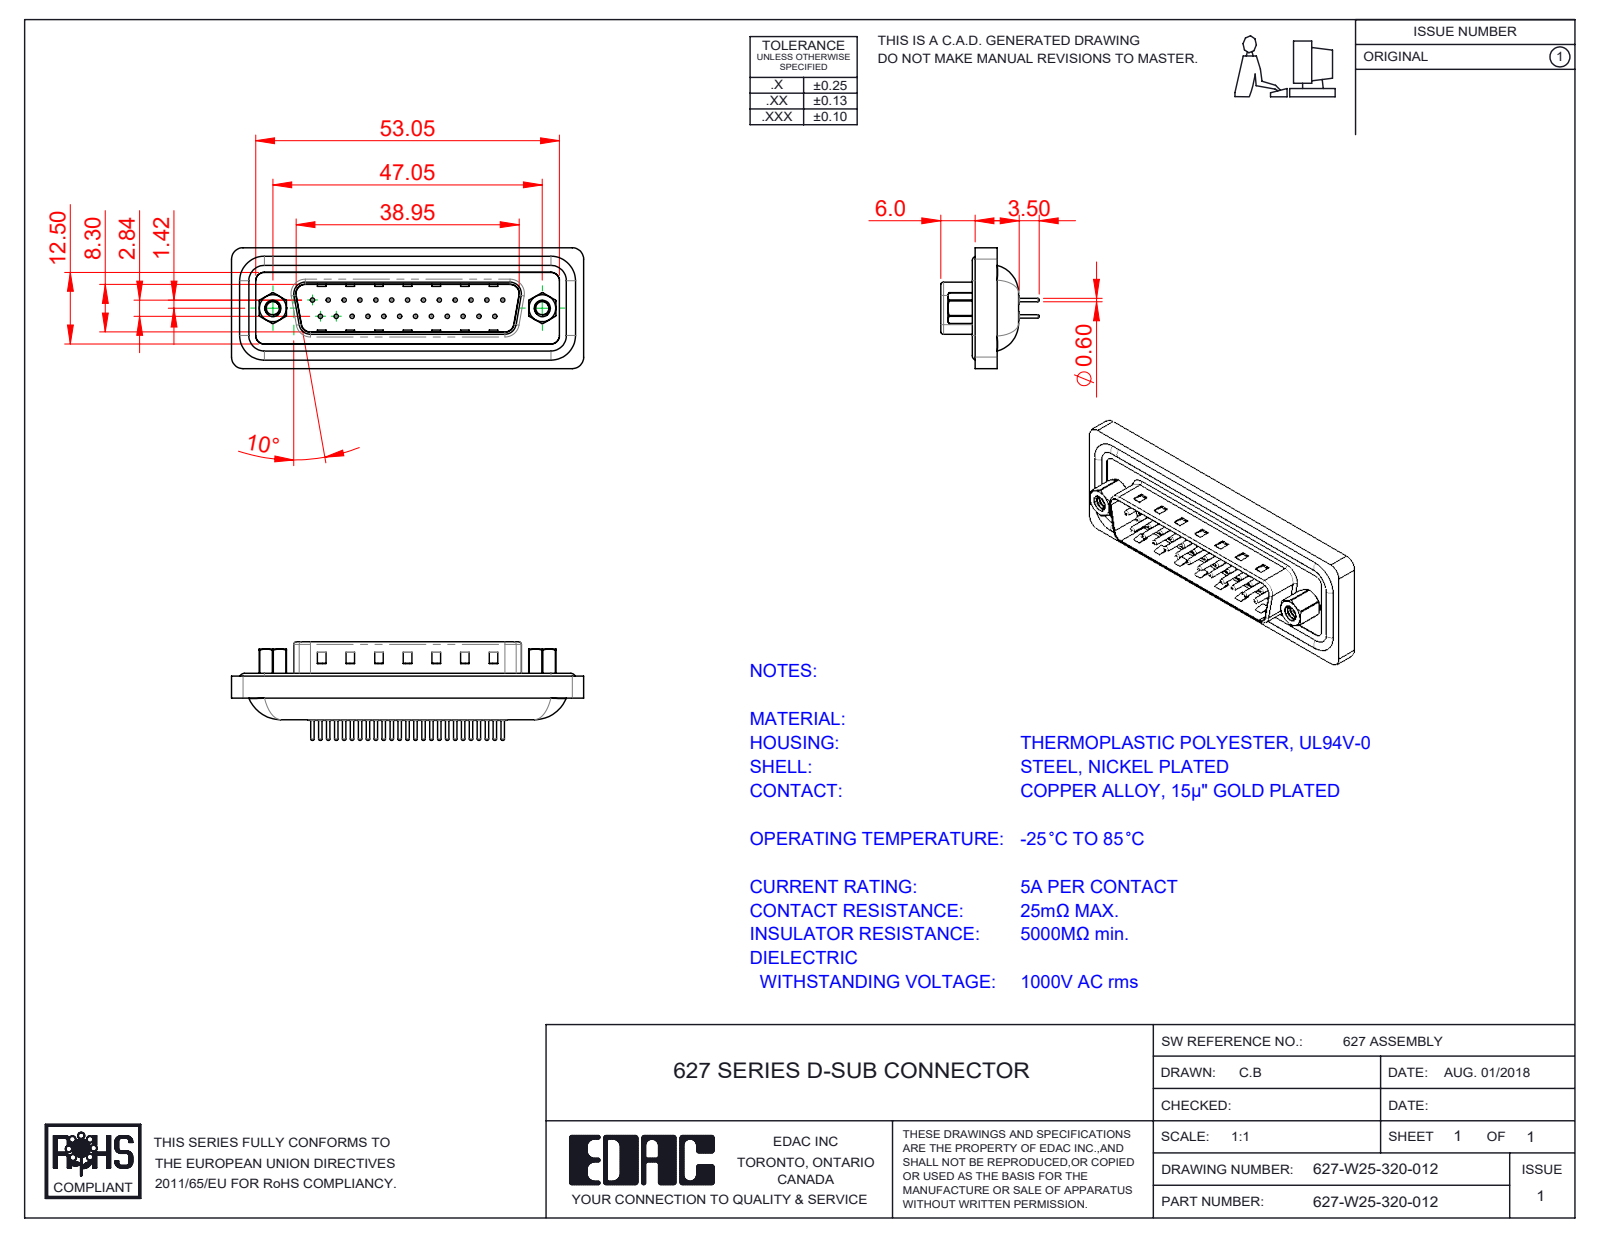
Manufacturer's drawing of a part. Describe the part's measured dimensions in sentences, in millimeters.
The part is named "627W Housing_25 Contacts; 627W Waterproof Housing_25 Contacts; 627W 4-40 Hex Standoff; 627W 4-40 Threaded Rivet (+4 more)". Its 3-D file was written by "SolidWorks 2020 (CONFIG_CONTROL_DESIGN)". It is 33 solids with 1495 faces: 380 planar, 620 cylindrical and 495 other. Overall it measures 61.5 by 21.1 by 17.2 millimeters. Its volume is 7 471 cubic millimeters and its surface area 11 062 square millimeters. Round holes: 25 of diameter 0.75, 25 of diameter 1.5, 25 of diameter 1.6, 25 of diameter 2, 2 of diameter 2.26, 2 of diameter 2.29, 2 of diameter 4, 2 of diameter 4.8, 2 of diameter 5. Round bosses or shafts: 25 of diameter 0.6, 7 of diameter 1.5, 4 of diameter 1.6, 2 of diameter 4.9, 2 of diameter 2.79. Partial cylindrical surfaces (rounded edges, fillets, slot ends): 16 of radius 2, 14 of radius 1.5, 8 of radius 0.5, 6 of radius 2.7, 4 of radius 0.9, 4 of radius 1.6, 4 of radius 4.3, 2 of radius 0.4. The main face-to-face distances are 0.75, 0.4, 1.1, 2.75, 3.75, 4.6, 4.1, 0.5, 5.65, 15.45. The hole center spacings are 3.16, 2.77, 5.54, 8.31, 11.08, 13.85, 5.04, 16.62.
